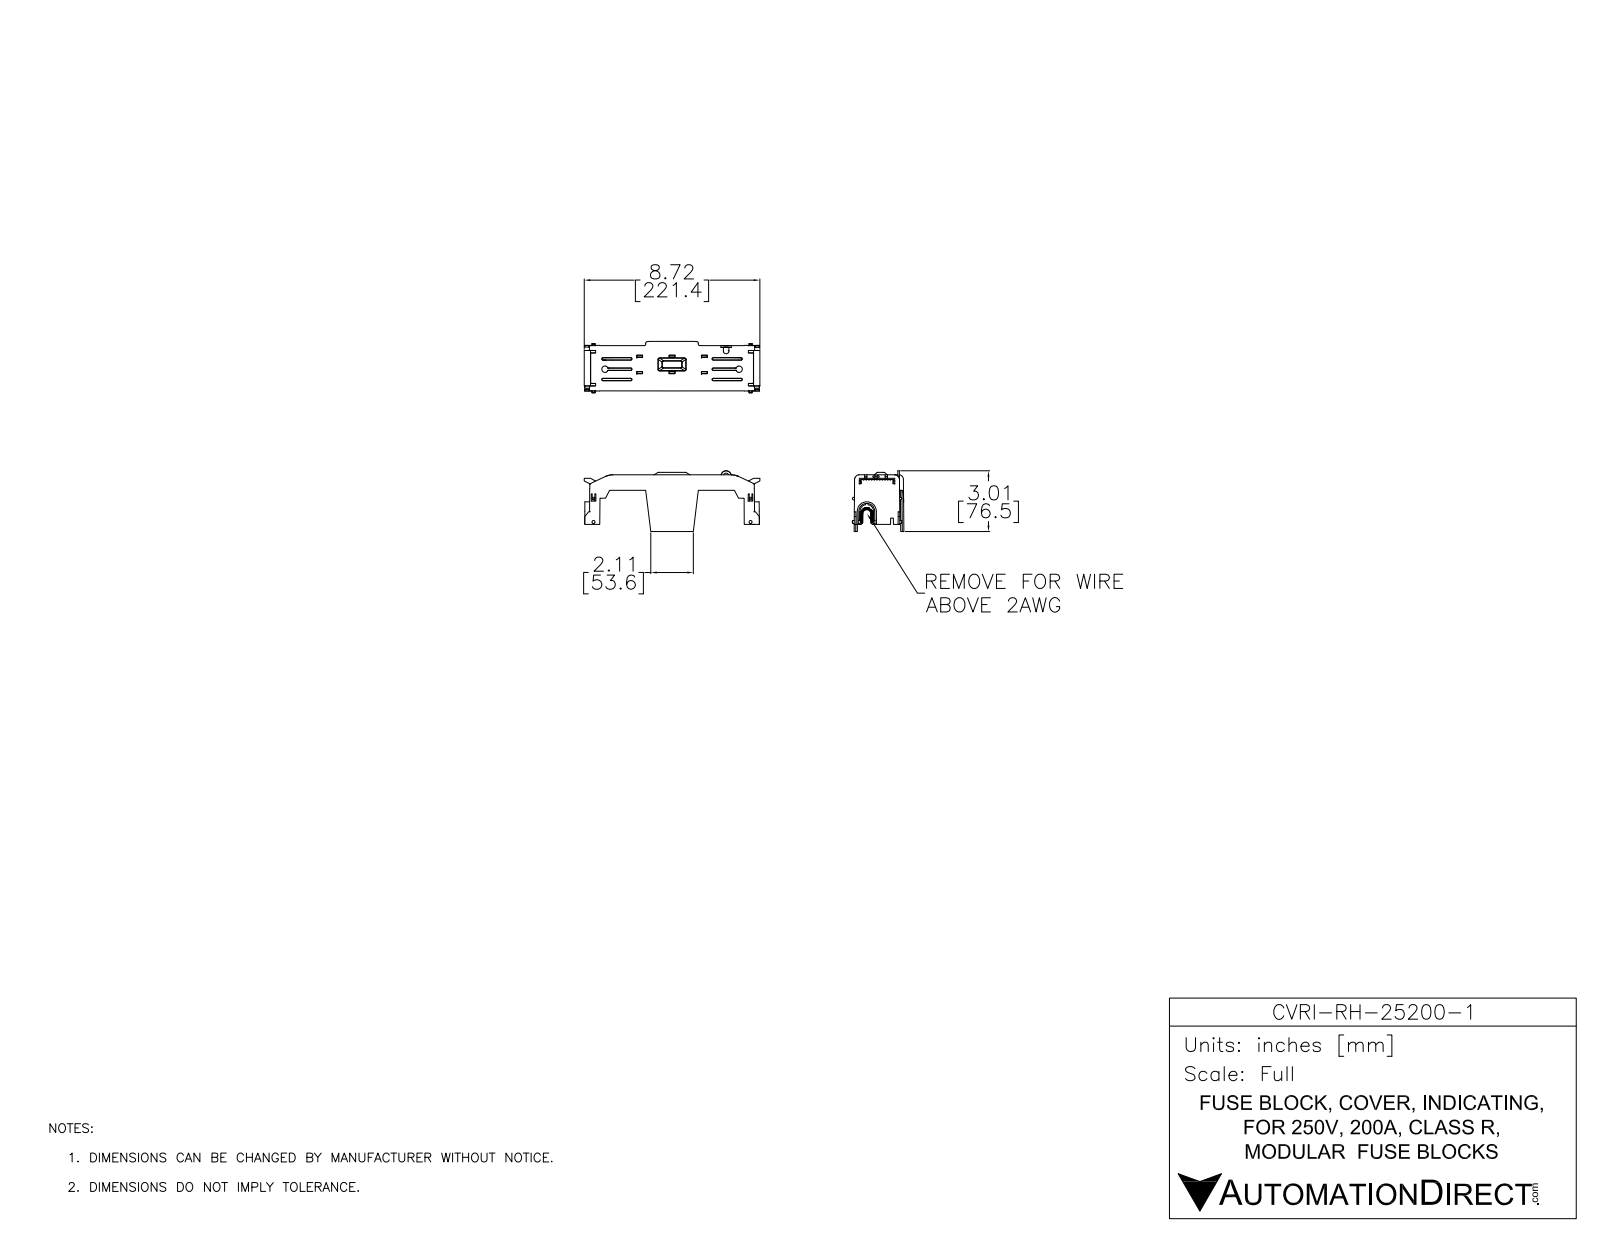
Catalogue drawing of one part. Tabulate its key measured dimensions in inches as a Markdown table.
| quantity | value |
| --- | --- |
| part name | CVRI-RH-25200-1 |
| STEP written by | SolidWorks 2017 (AUTOMOTIVE_DESIGN) |
| units | inches |
| bodies | 1 solid, 1406 faces (950 planar, 105 cylindrical, 351 other) |
| overall size | 8.715 × 3.012 × 2.554 |
| volume | 4.617 in³ |
| surface area | 125 in² |
| round holes (diameter × count) | 0.276 × 1 |
| partial cylindrical surfaces (radius × count) | 0.039 × 16, 0.236 × 9, 0.118 × 8, 0.157 × 7, 0.079 × 6, 0.01 × 2, 0.02 × 2, 0.63 × 2 |
| main face-to-face distances | 0.079, 0.197, 0.118, 0.276, 0.803, 0.604, 1.661, 1.74, 1.286, 1.365 |
